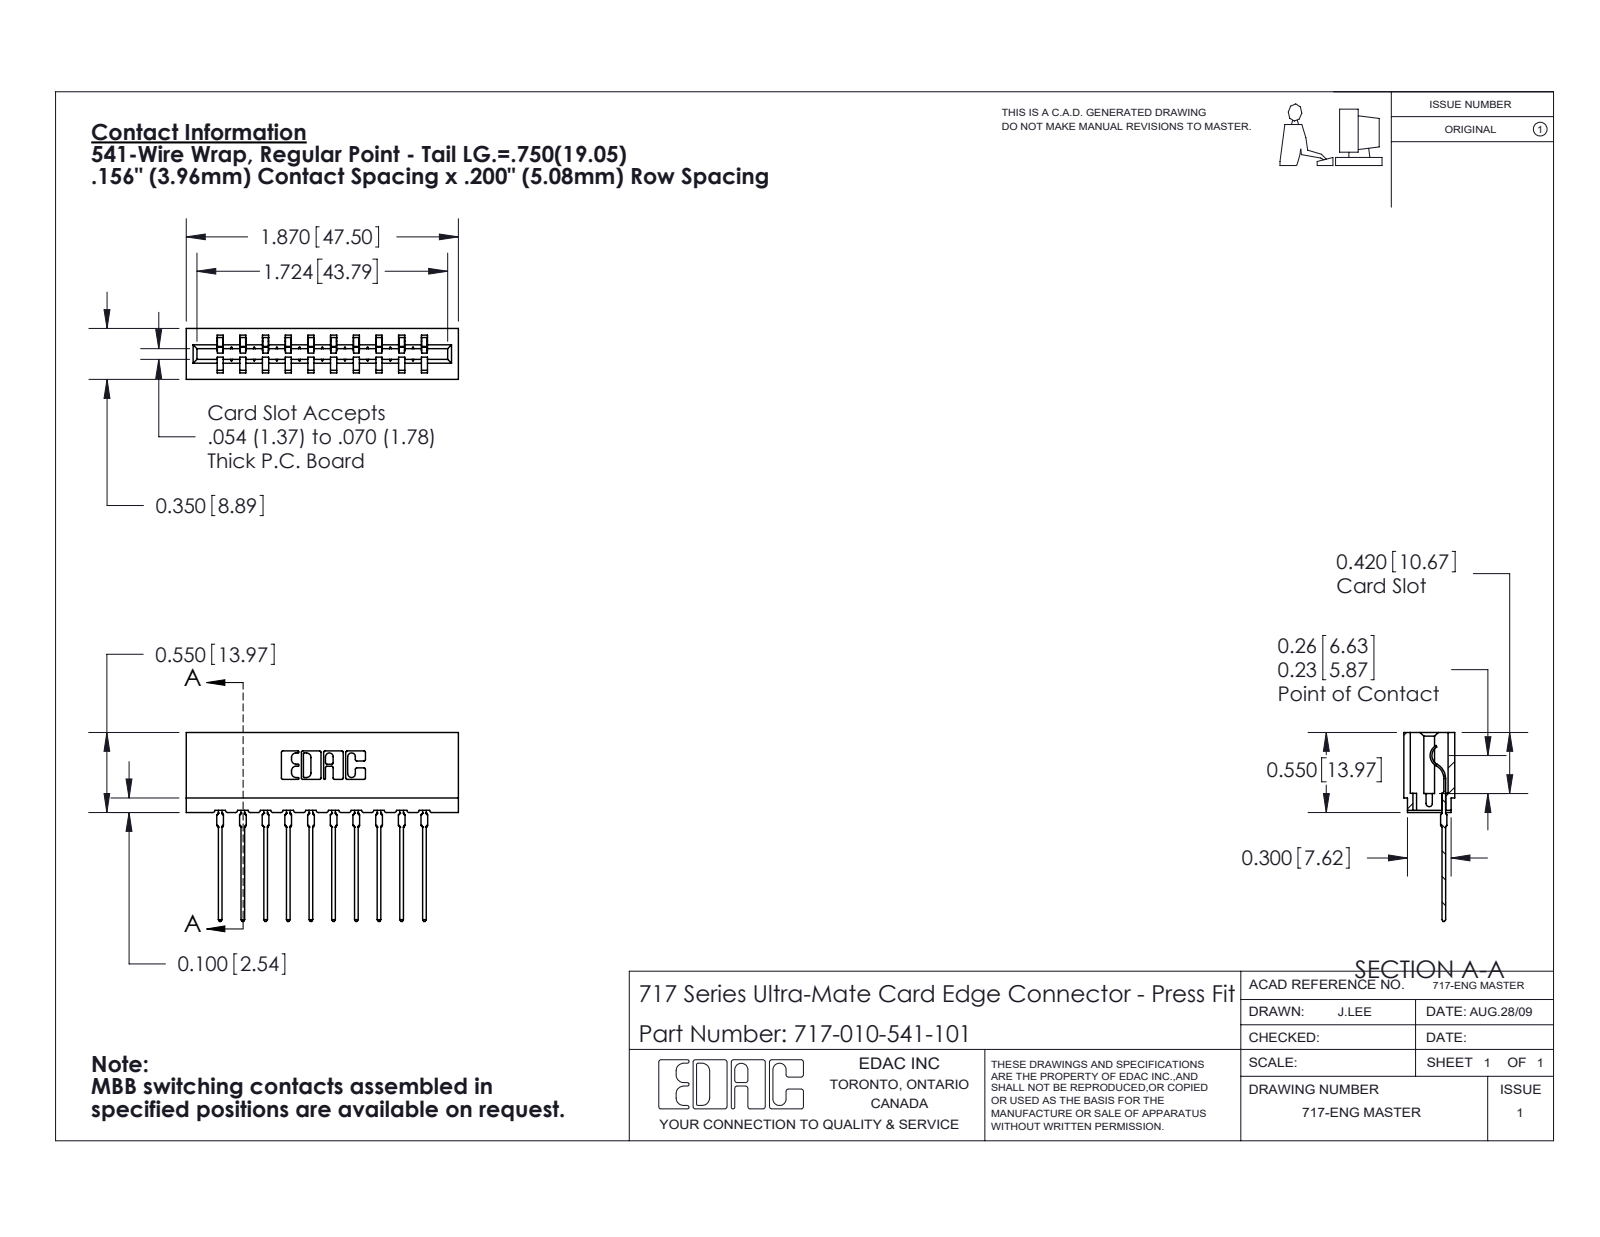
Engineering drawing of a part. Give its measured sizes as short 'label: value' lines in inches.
name: 717 Part_Insulator Option - 06; 745-292-001_541; 717-010-541-101
written by: SolidWorks 2020 (CONFIG_CONTROL_DESIGN)
unit: in
bodies: 11 solids, 1224 faces (734 planar, 230 cylindrical, 260 other)
size: 1.87 × 1.299 × 0.35
volume: 0.256 in³; area: 8.929 in²
rounds: 22× R0.01, 20× R0.015, 20× R0.021, 6× R0.007, 6× R0.031, 4× R0.005, 4× R0.011, 3× R0.026
face distances: 0.156, 0.212, 0.138, 0.624, 0.35, 0.198, 0.468, 0.312, 0.354, 0.312
